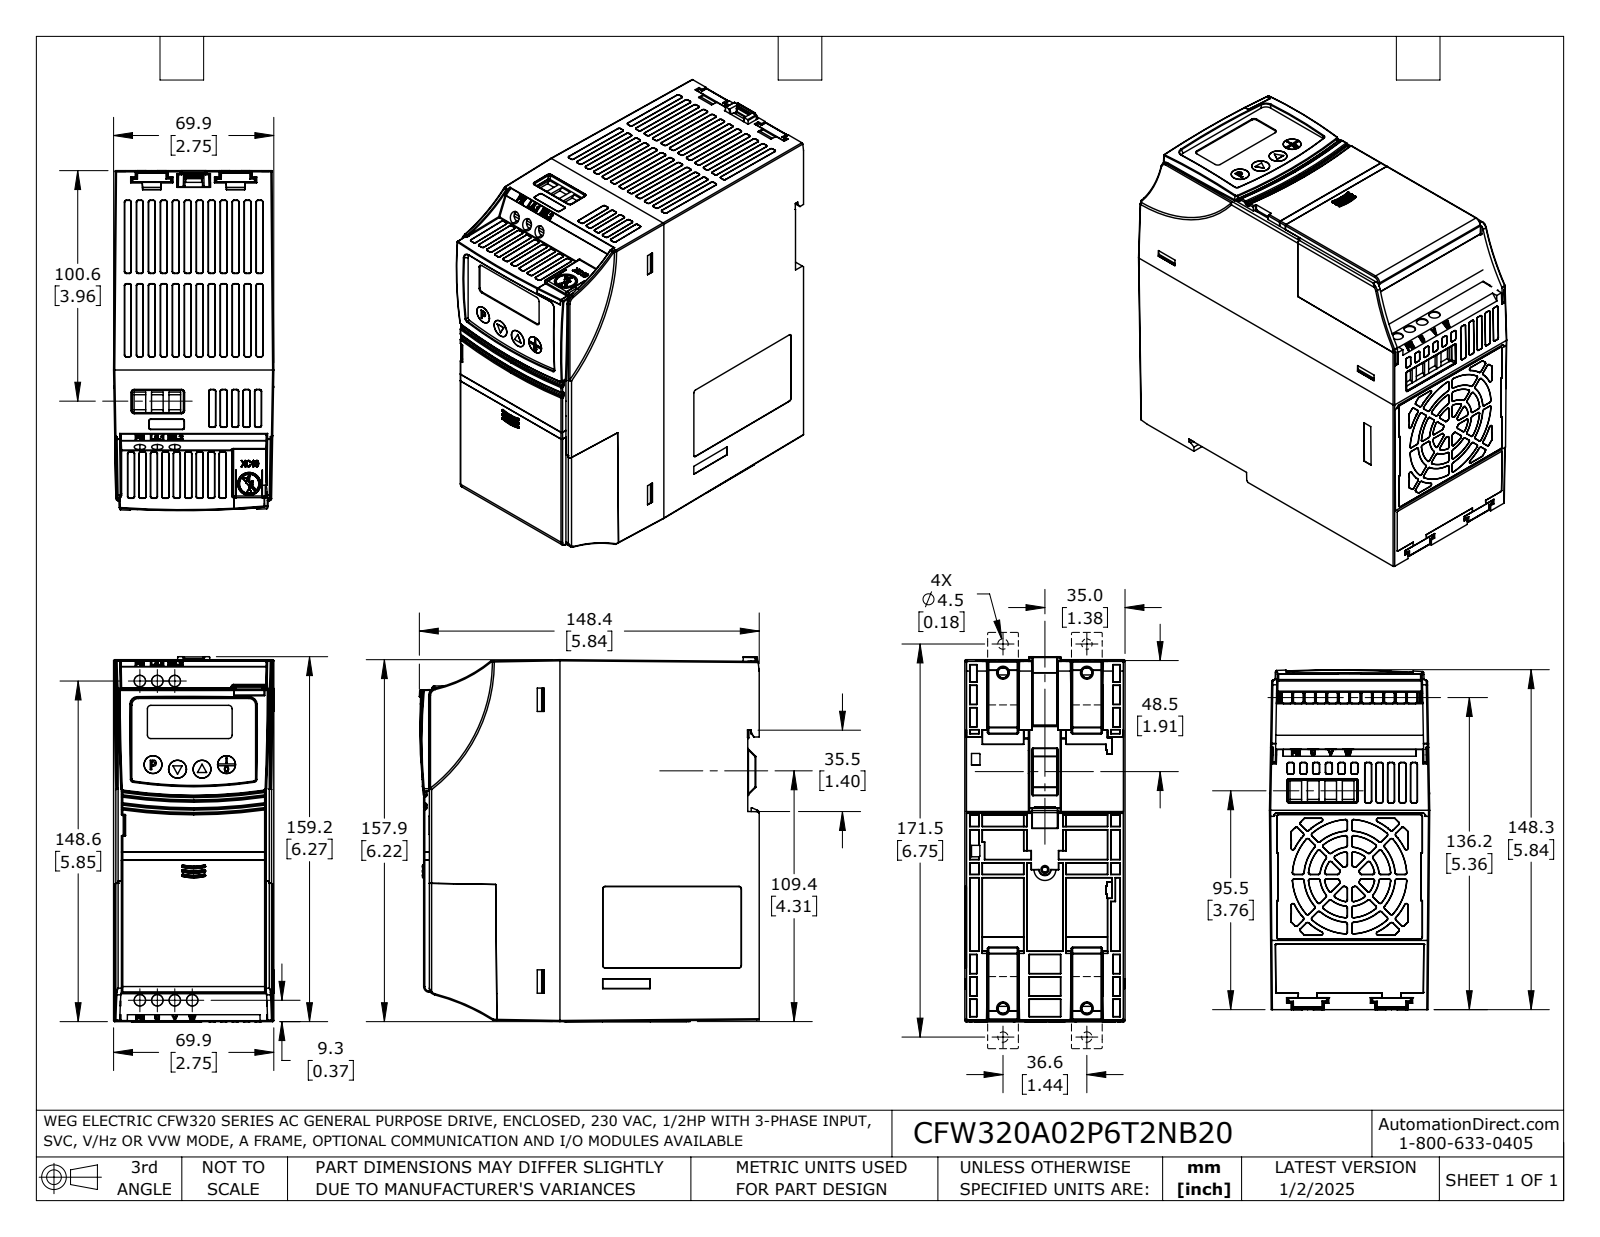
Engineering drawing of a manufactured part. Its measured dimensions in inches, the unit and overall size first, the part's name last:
Units: inches
Overall size (bounding box): 6.269 × 5.841 × 2.754
Round holes (diameter × count): ⌀0.197 ×3
Partial cylindrical surfaces — rounded edges, fillets, slot ends (radius × count): R0.012 ×327, R0.02 ×150, R0.039 ×13, R0.03 ×5, R0.118 ×3, R0.01 ×2, R0.098 ×1, R0.126 ×1
Main face-to-face distances: 0.07, 0.055, 0.019, 0.05, 6, 5.33, 5.275, 5.571, 5.516, 0.241
Hole centre spacings: 0.3, 0.6
Volume: 15.24 in³ · Surface area: 309 in²
Bodies: 6 solids, 3715 faces (1587 planar, 853 cylindrical, 1275 other)
Part name (STEP PRODUCT): CFW320A02P6T2NB20
STEP written by: SolidWorks 2021 (AUTOMOTIVE_DESIGN)
